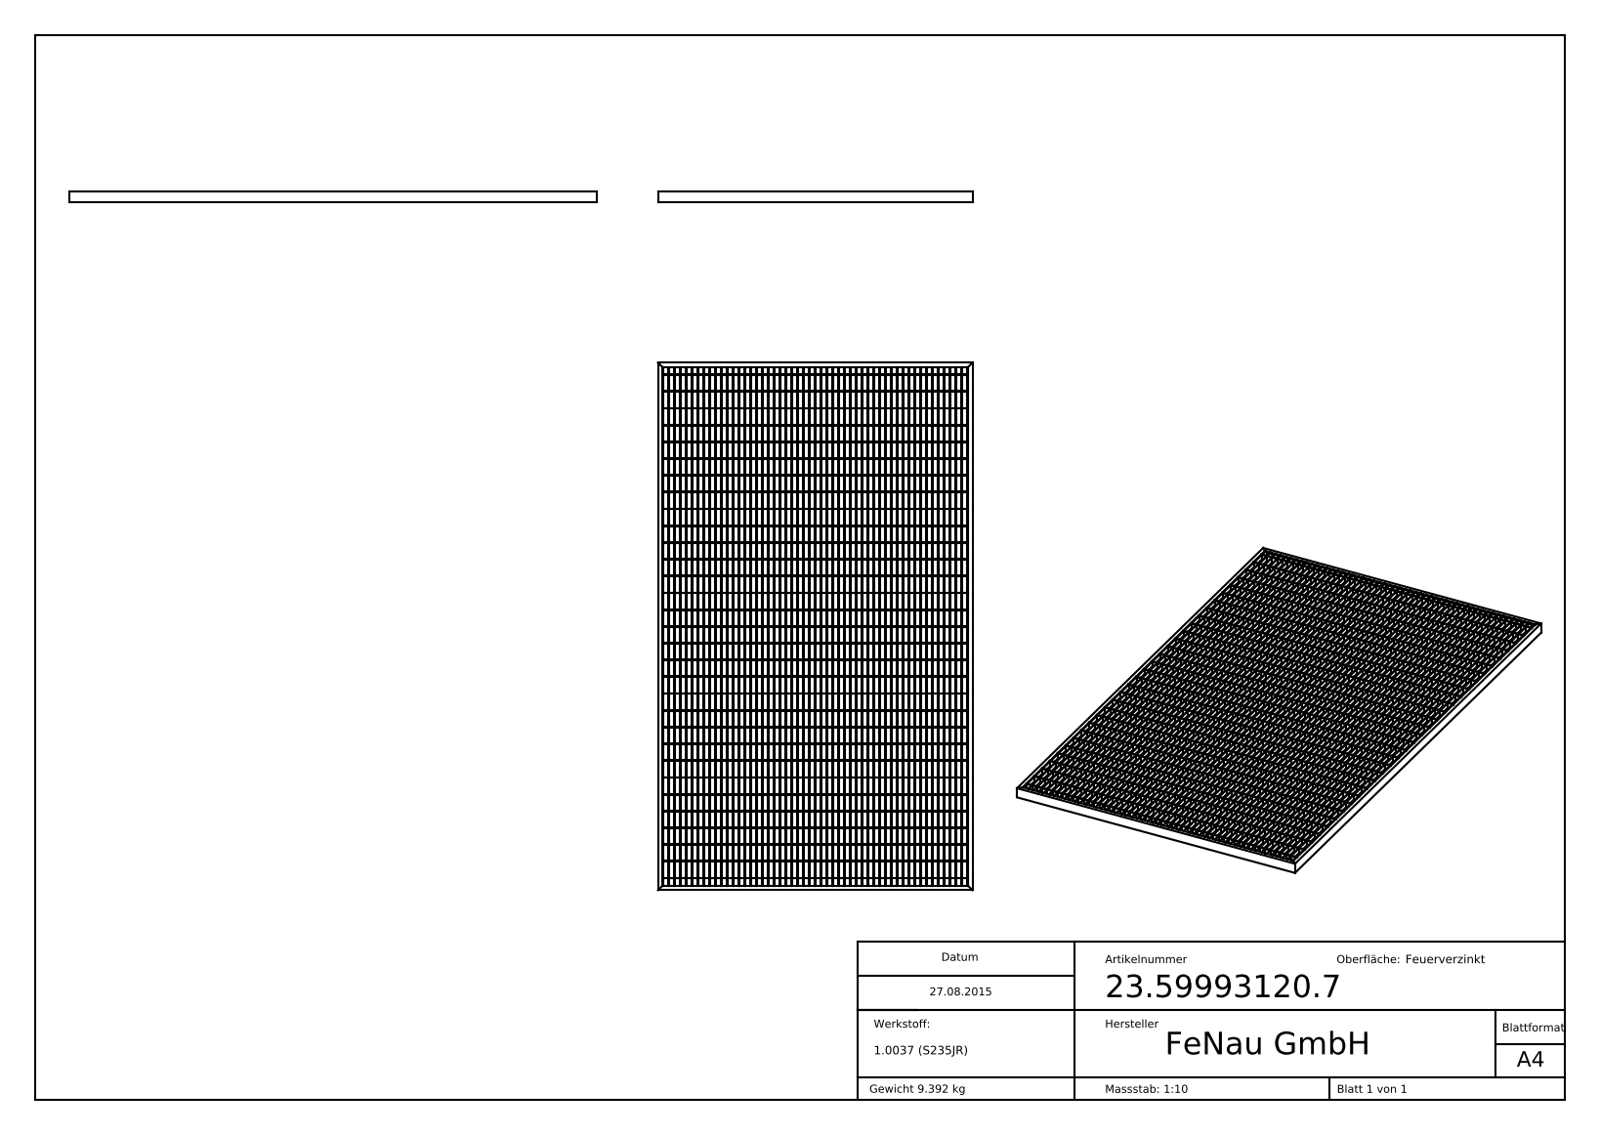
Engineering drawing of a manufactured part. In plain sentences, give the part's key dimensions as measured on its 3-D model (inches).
The part is named "23-59993120-7". Its 3-D file was written by "SolidWorks 2015 (CONFIG_CONTROL_DESIGN)". It is 1 solid with 5568 faces: 5568 planar, 0 cylindrical and 0 other. Overall it measures 38.976 by 23.228 by 0.787 inches. Its volume is 73.47 cubic inches and its surface area 3 116 square inches. The main face-to-face distances are 1.24, 2.48, 3.72, 4.961, 0.433, 0.866, 6.201, 1.299, 1.732, 7.441.
